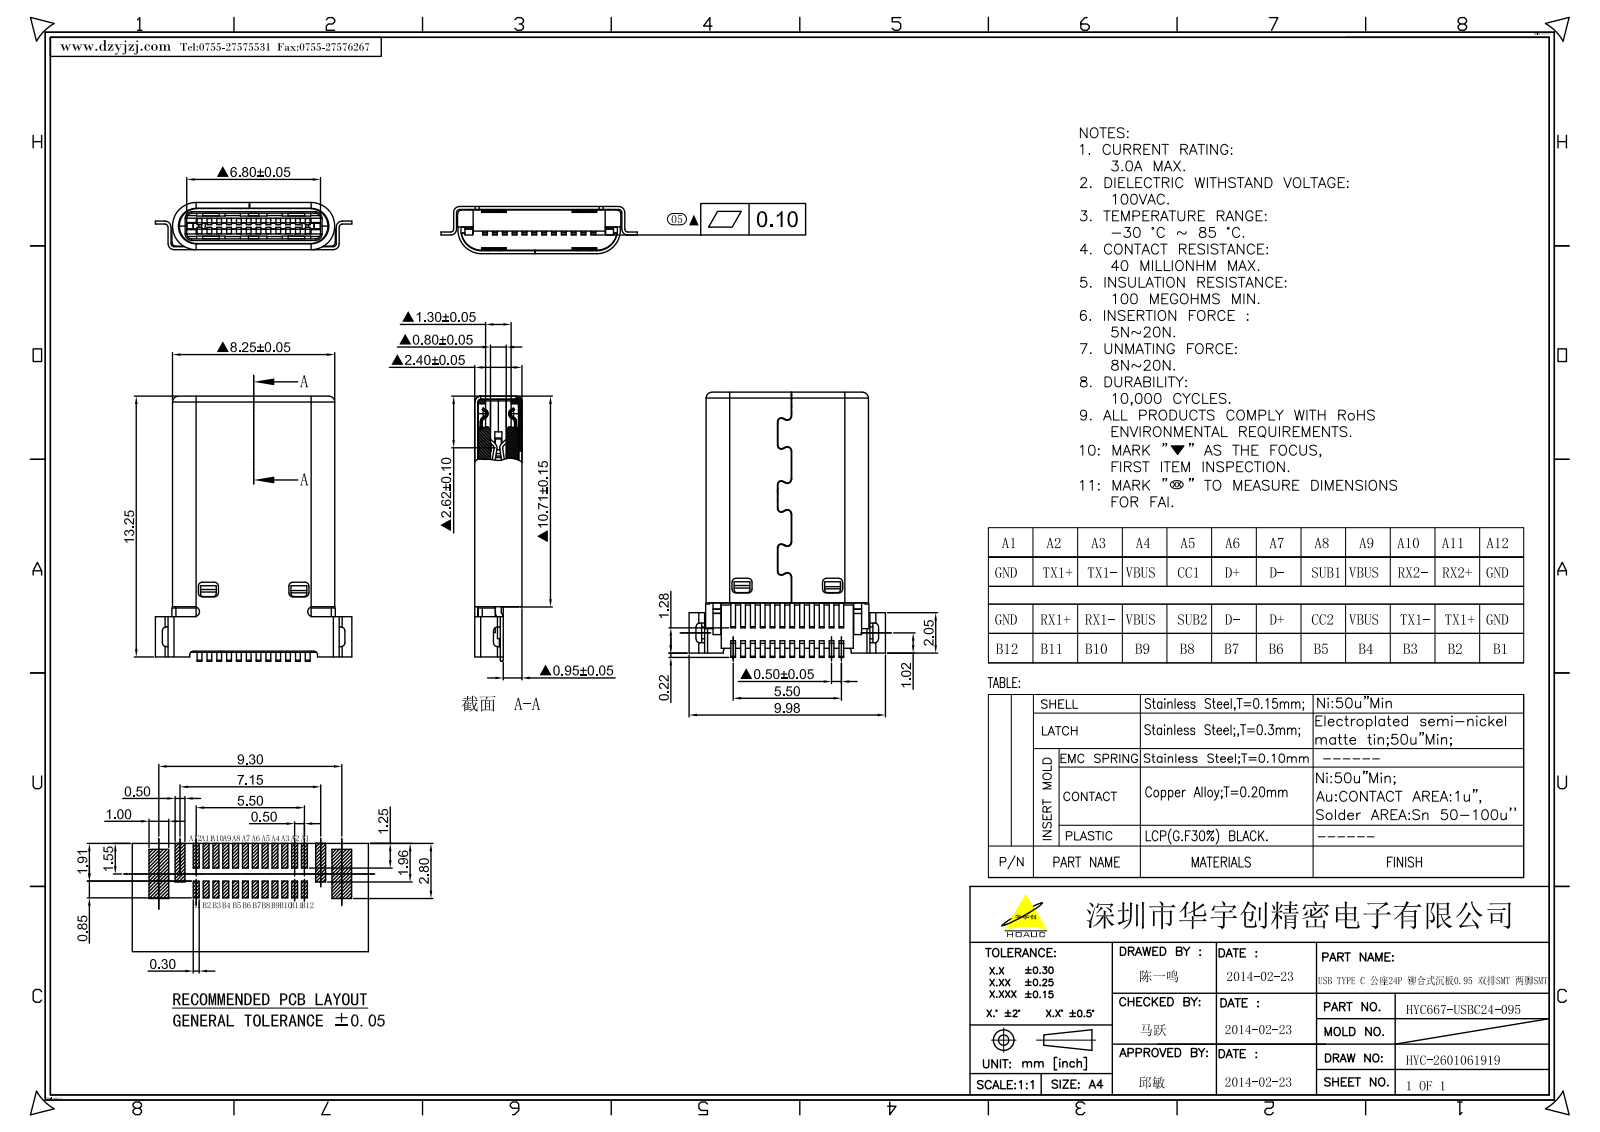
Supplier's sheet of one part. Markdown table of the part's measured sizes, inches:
| quantity | value |
| --- | --- |
| part name | TANPIAN-PLASTIC_1_2__2_1_3_1__3 |
| STEP written by | CREO PARAMETRIC BY PTC INC, 2022073 (CONFIG_CONTROL_DESIGN) |
| units | inches |
| bodies | 1 solid, 755 faces (569 planar, 182 cylindrical, 4 other) |
| overall size | 0.53 × 0.393 × 0.094 |
| volume | 0.011 in³ |
| surface area | 0.752 in² |
| partial cylindrical surfaces (radius × count) | 0.008 × 30, 0.006 × 13, 0.01 × 12, 0.012 × 10, 0.007 × 6, 0.009 × 6, 0.004 × 4, 0.005 × 4 |
| main face-to-face distances | 0.031, 0.094, 0.063, 0.051, 0.026, 0.045, 0.057, 0.022, 0.02, 0.043 |
